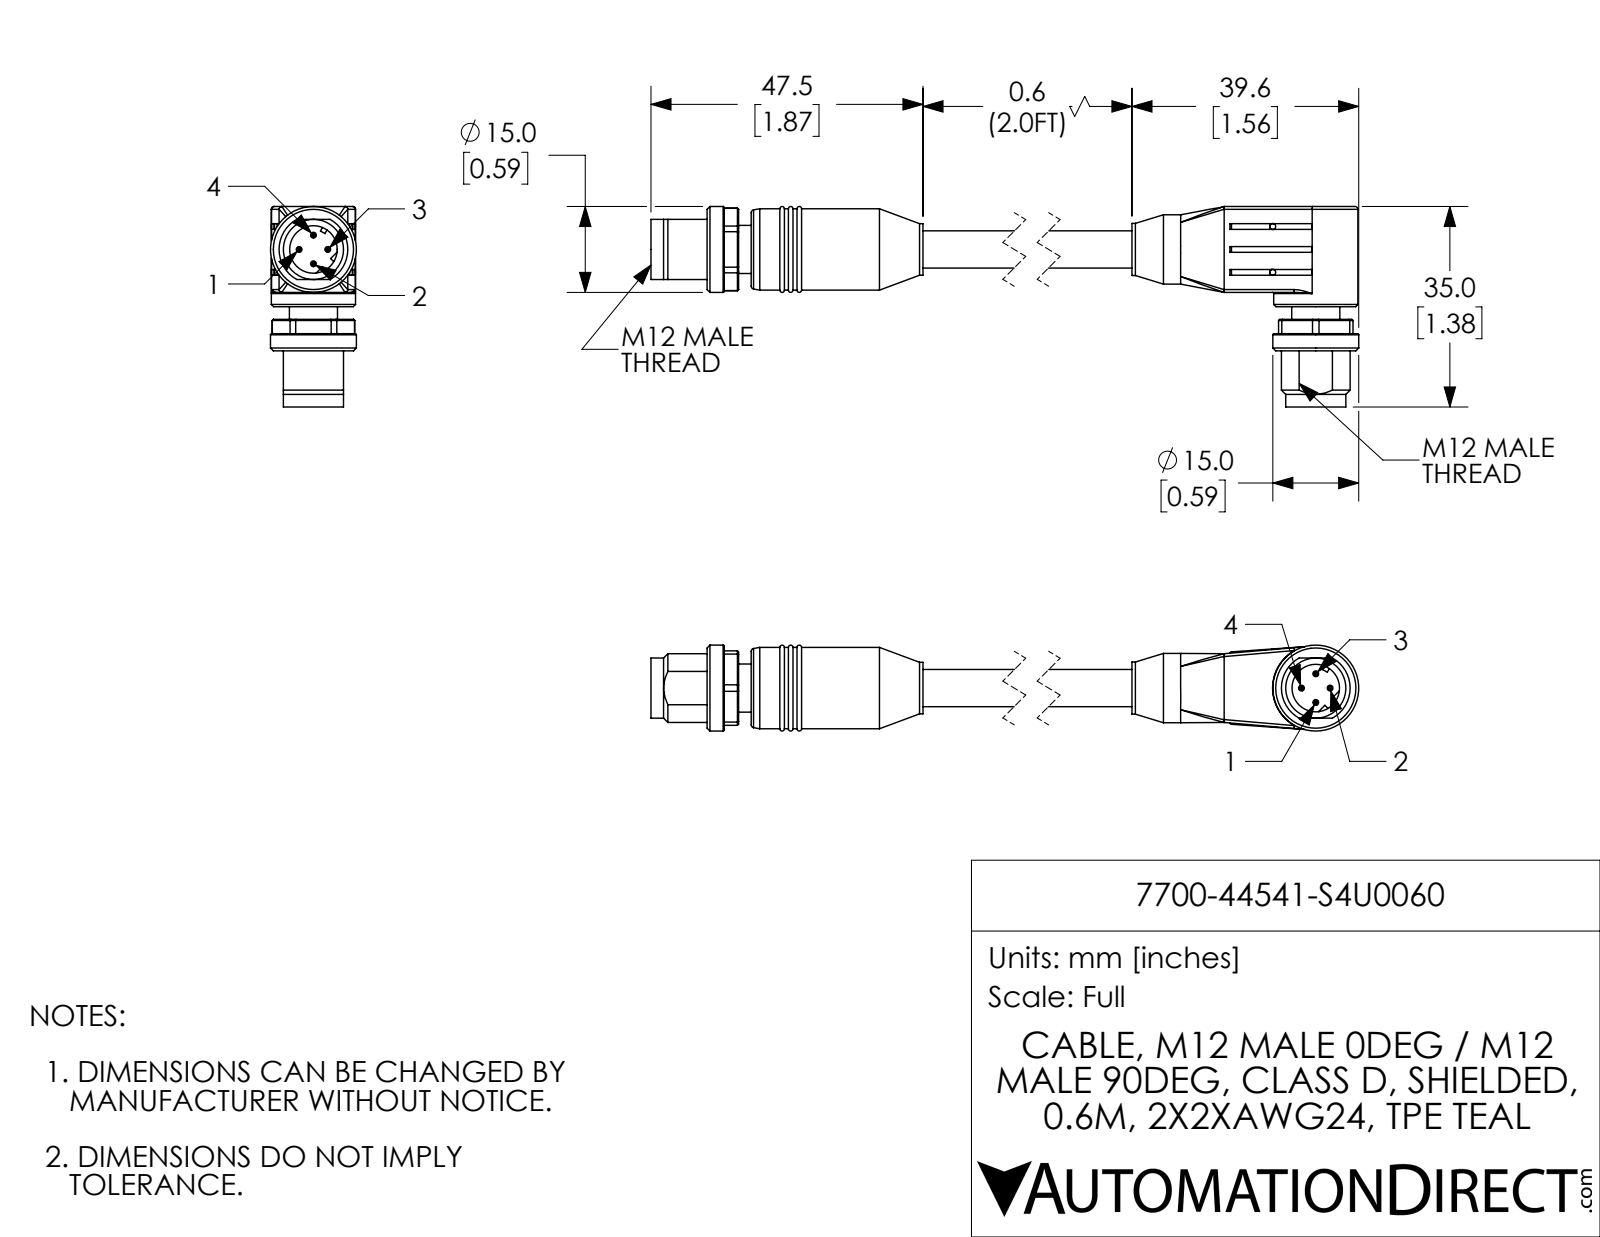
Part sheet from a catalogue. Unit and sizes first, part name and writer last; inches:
Units: inches
Overall size (bounding box): 5.476 × 1.378 × 0.591
Round holes (diameter × count): ⌀0.041 ×4, ⌀0.327 ×2, ⌀0.189 ×1
Round bosses / shafts (diameter × count): ⌀0.039 ×8, ⌀0.591 ×2, ⌀0.413 ×2, ⌀0.331 ×2, ⌀0.579 ×1, ⌀0.559 ×1, ⌀0.476 ×1, ⌀0.358 ×1
Partial cylindrical surfaces — rounded edges, fillets, slot ends (radius × count): R0.02 ×4, R0.012 ×2, R0.236 ×2, R0.283 ×2
Main face-to-face distances: 0.689, 0.087, 0.098, 0.185, 0.591, 0.035, 0.252, 0.339, 0.217, 0.303
Hole centre spacings: 0.315
Volume: 0.955 in³ · Surface area: 10.92 in²
Bodies: 2 solids, 284 faces (114 planar, 90 cylindrical, 80 other)
Part name (STEP PRODUCT): 7700-44541-S4U0060_MALE90; 7700-44541-S4U0060_MALE; 7700-44541-S4U0060
STEP written by: SolidWorks 2017 (AUTOMOTIVE_DESIGN)
